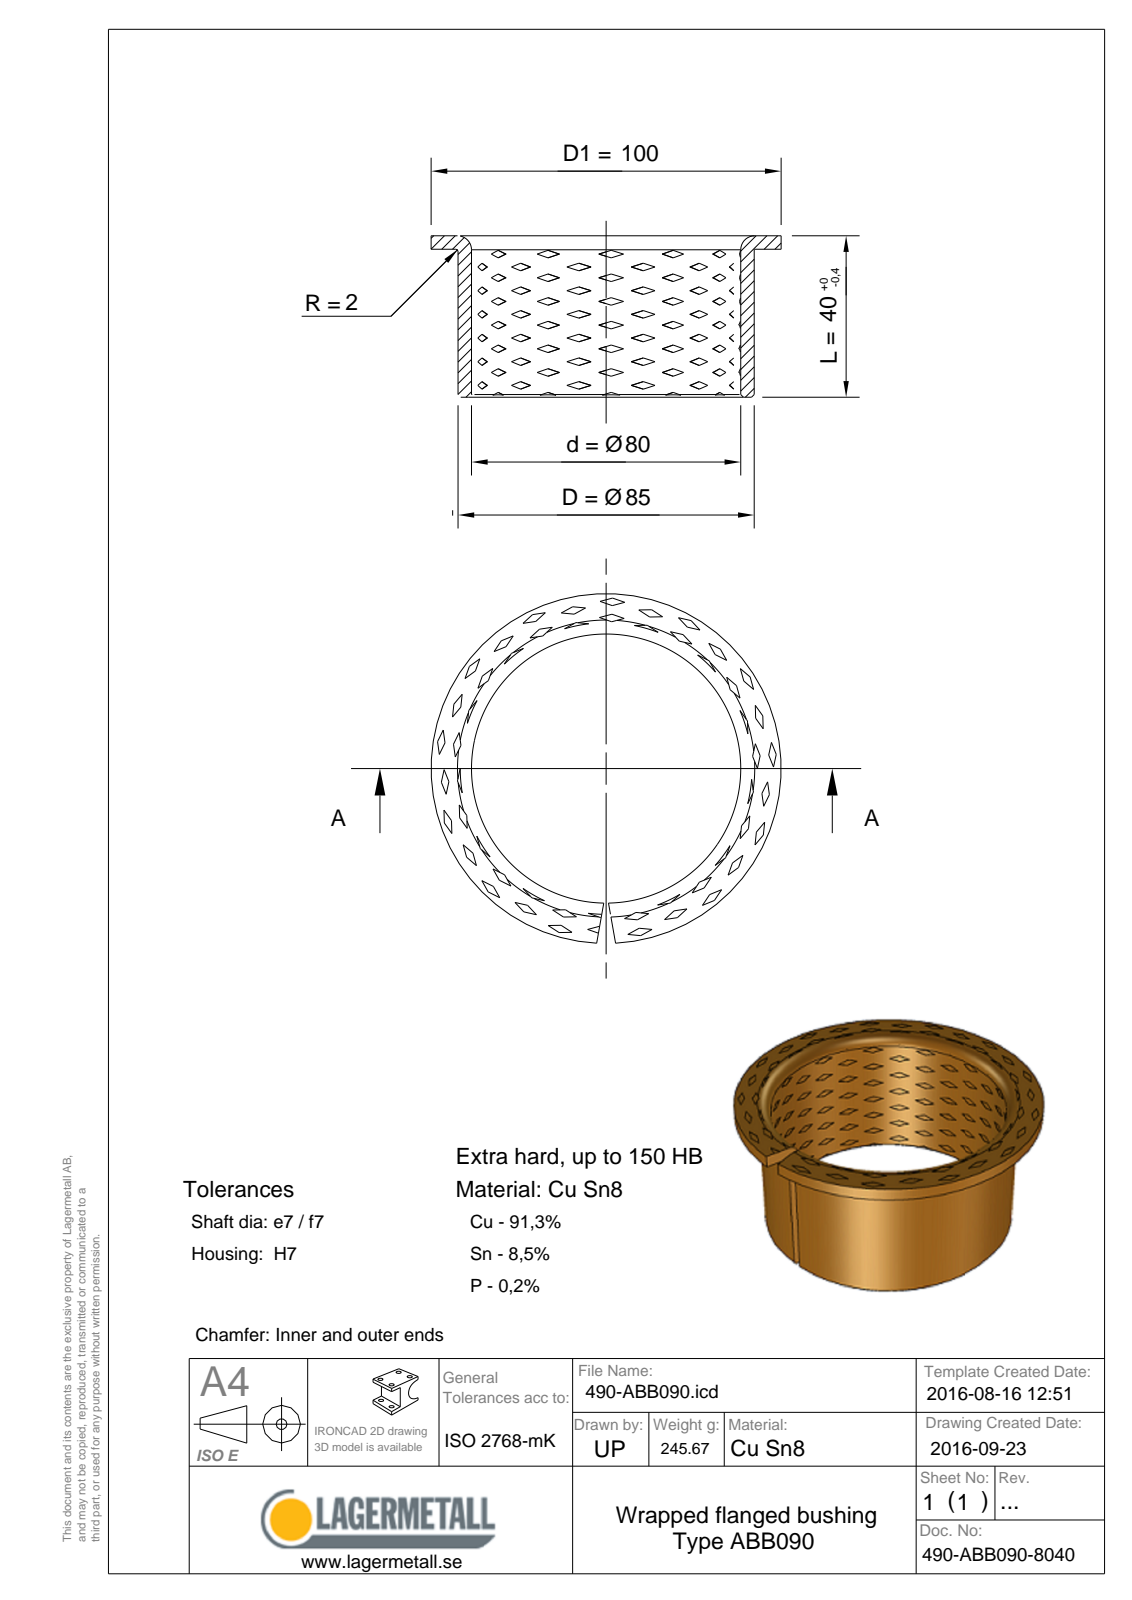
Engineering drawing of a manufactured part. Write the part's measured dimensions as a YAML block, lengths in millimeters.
step_written_by: "Spatial InterOp 3D (CONFIG_CONTROL_DESIGN)"
units: millimeters
bodies: {solids: 1, faces: 25, planar: 5, cylindrical: 8, other: 12}
overall_size: [100, 100, 40]
volume: 30329
surface_area: 25808
round_holes:
  - {diameter: 80, count: 1}
round_bosses_or_shafts:
  - {diameter: 100, count: 1}
  - {diameter: 85, count: 1}
face_to_face_distances: [2.5, 37.5, 40]
